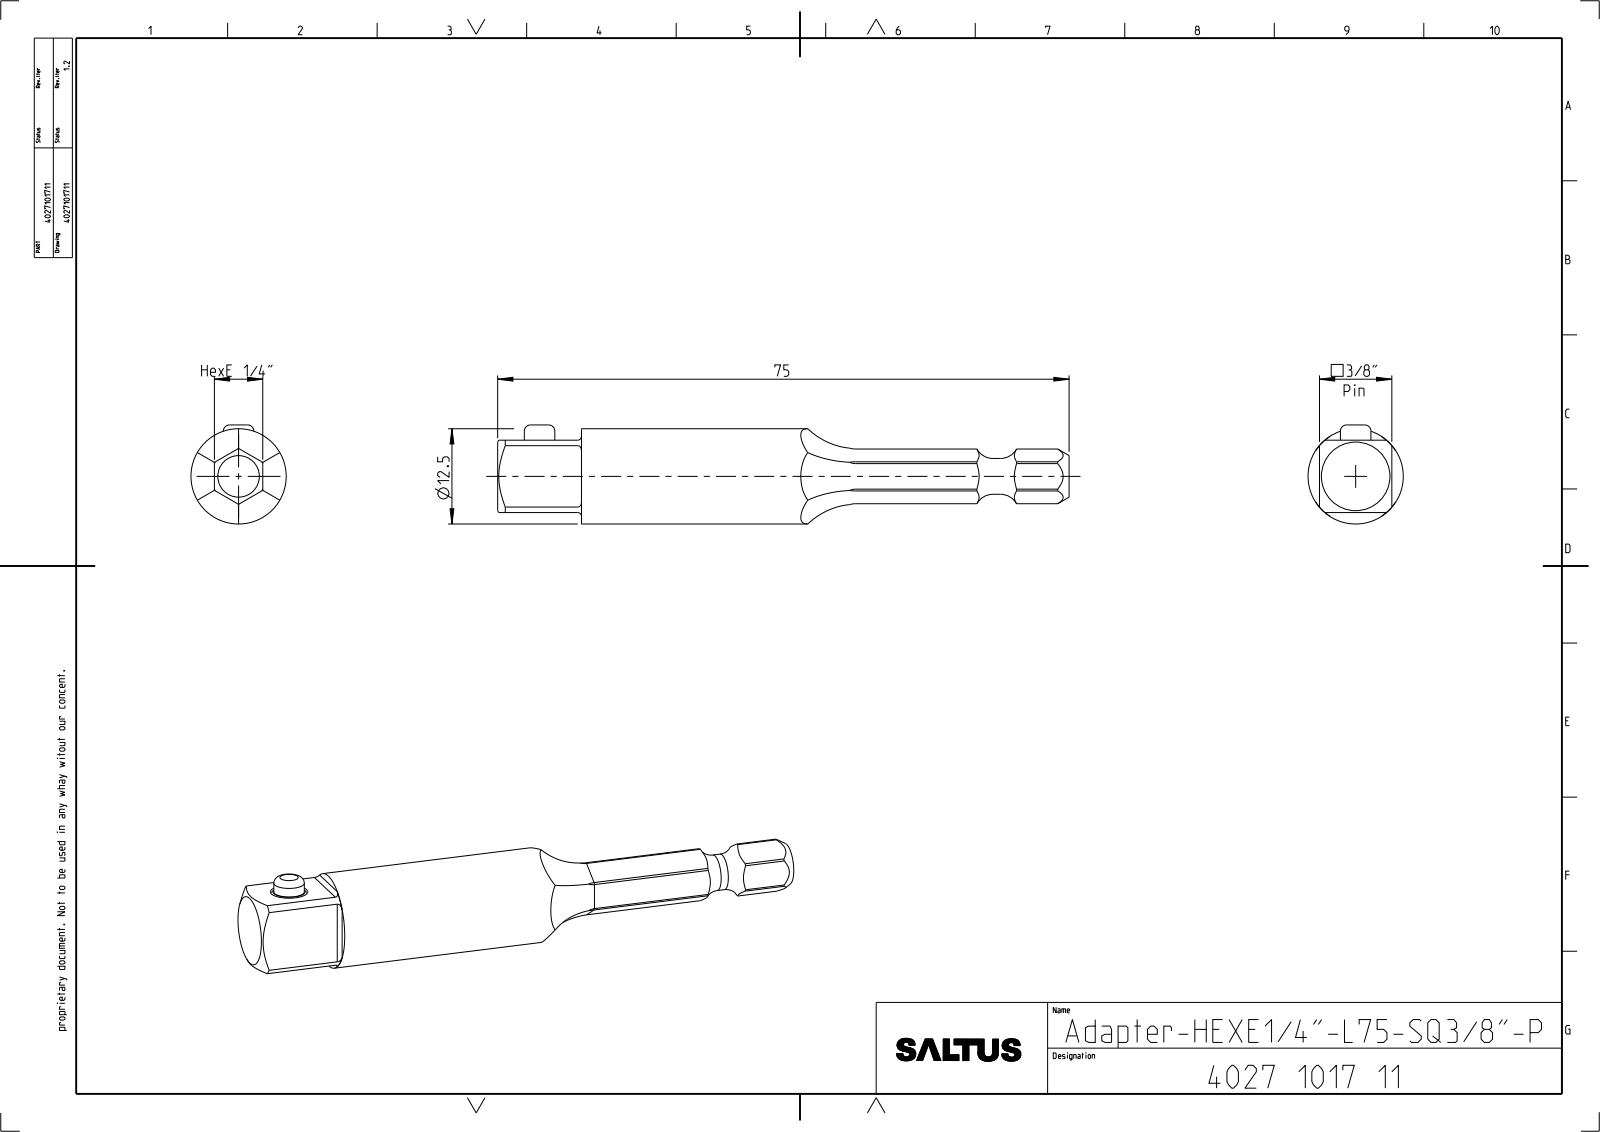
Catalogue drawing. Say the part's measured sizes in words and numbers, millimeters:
The part is named "4027101711". Its 3-D file was written by "CREO PARAMETRIC BY PTC INC, 2022414 (CONFIG_CONTROL_DESIGN)". It is 2 solids with 80 faces: 24 planar, 36 cylindrical and 20 other. Overall it measures 75 by 13 by 12.5 millimeters. Its volume is 5 817 cubic millimeters and its surface area 2 724 square millimeters. Round holes: 1 of diameter 4.9. Round bosses or shafts: 1 of diameter 12.5, 1 of diameter 4.8, 1 of diameter 4.7, 1 of diameter 4. Partial cylindrical surfaces (rounded edges, fillets, slot ends): 6 of radius 10, 4 of radius 0.5, 1 of radius 3.59, 1 of radius 6.22. The main face-to-face distances are 6.34, 1.58, 7.92, 9.5, 6.36, 3.25, 75, 3, 6.5, 64.
